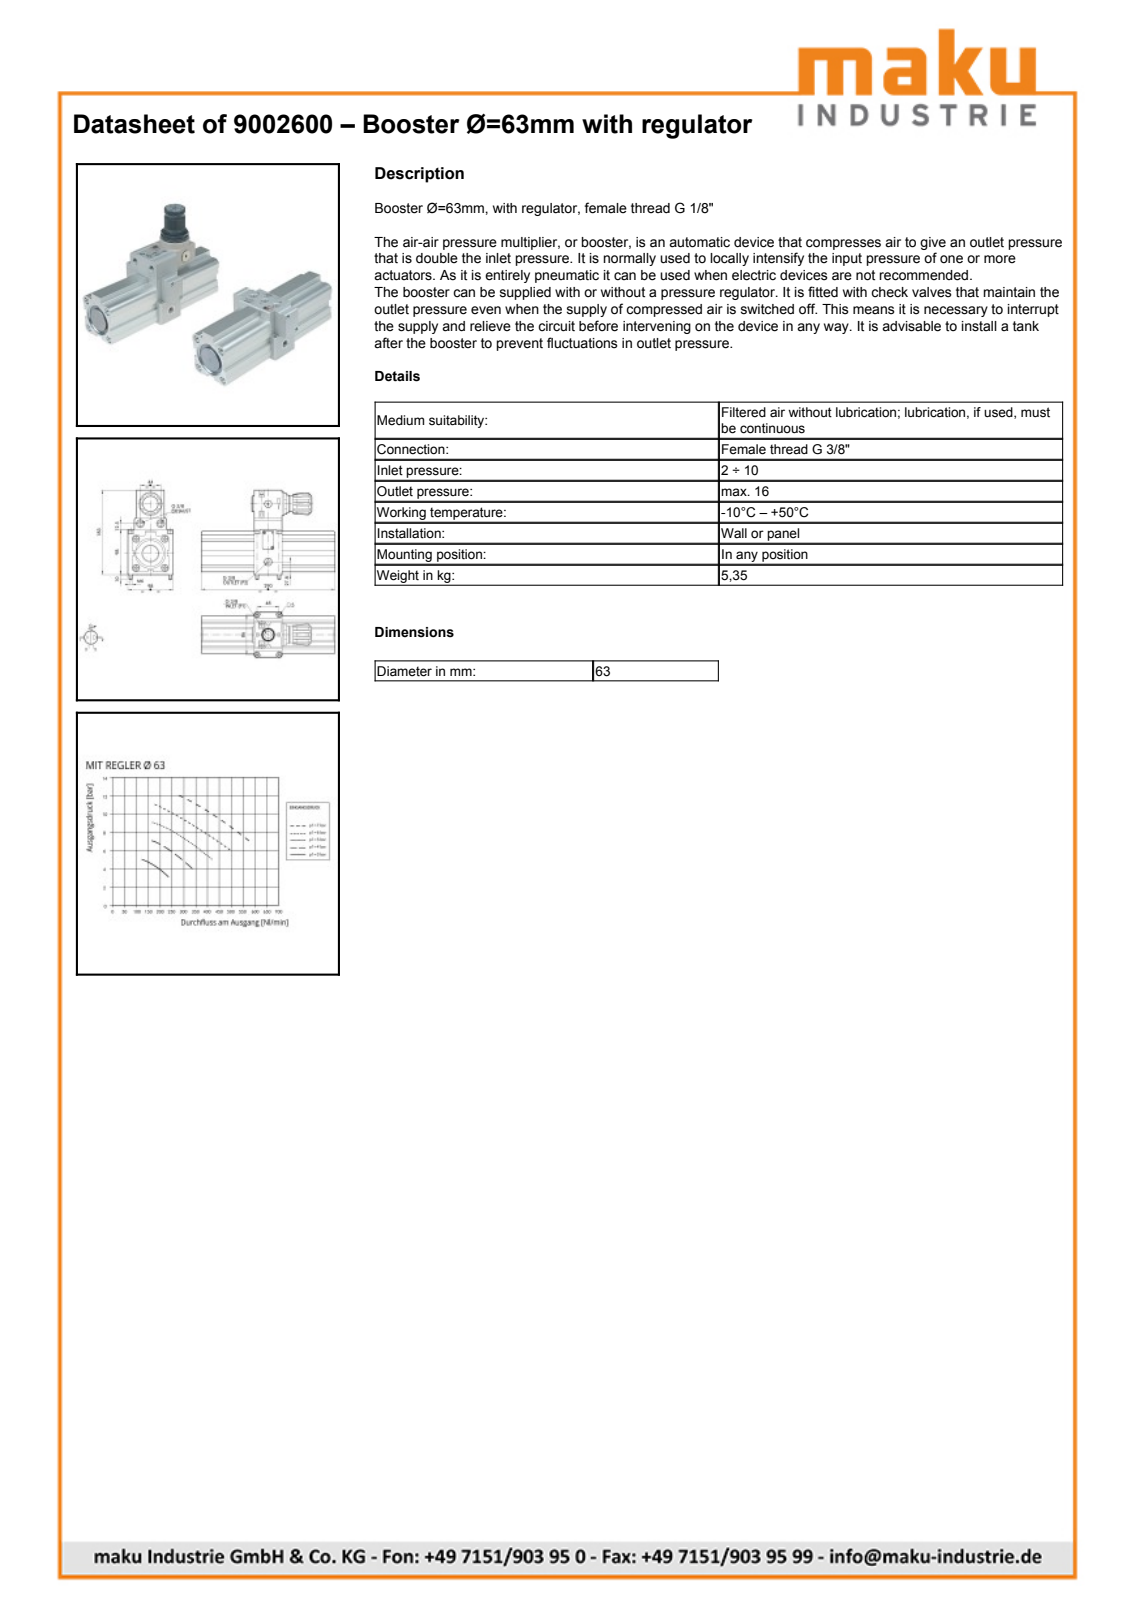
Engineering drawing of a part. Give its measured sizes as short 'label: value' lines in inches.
name: 9002600; 9002300; 63-regulator-unit; Body 3/8 (+4 more)
written by: PARTsolutions (AUTOMOTIVE_DESIGN)
unit: in
bodies: 9 solids, 751 faces (488 planar, 186 cylindrical, 77 other)
size: 11.417 × 7.614 × 3.858
volume: 143.8 in³; area: 313.4 in²
holes: 6× ⌀0.589, 4× ⌀0.177, 4× ⌀0.236, 4× ⌀0.591, 2× ⌀0.118, 2× ⌀0.128, 2× ⌀0.163, 2× ⌀0.217, 2× ⌀0.354, 1× ⌀0.337, 1× ⌀0.63, 1× ⌀0.921
bosses: 4× ⌀0.394, 4× ⌀0.335, 4× ⌀0.236, 4× ⌀0.197, 1× ⌀1.969, 1× ⌀1.496, 1× ⌀1.378, 1× ⌀1.346
rounds: 12× R0.008, 12× R0.02, 6× R0.197, 4× R0.157, 4× R0.177, 4× R0.236, 4× R0.354, 2× R0.118
face distances: 0.118, 3.858, 0.394, 2.362, 0.386, 3.472, 0.079, 3.087, 3.551, 3.433
hole spacings: 0.965, 1.364, 1.726, 2.441, 0.028, 0.22, 0.437, 0.63
